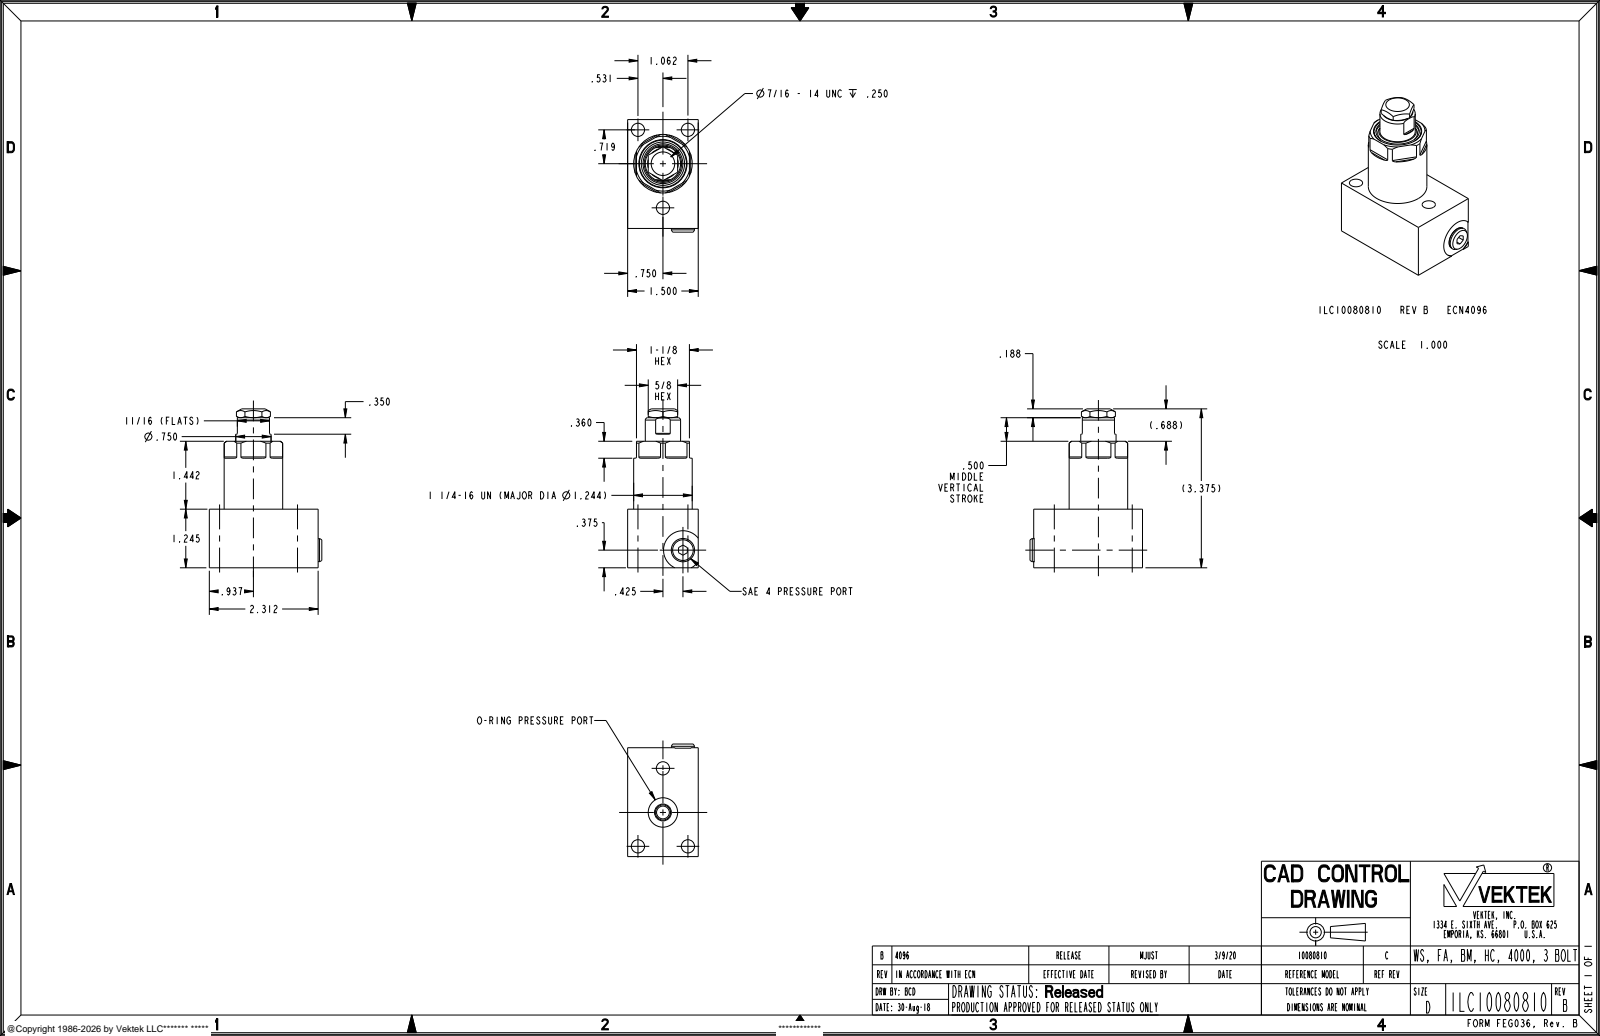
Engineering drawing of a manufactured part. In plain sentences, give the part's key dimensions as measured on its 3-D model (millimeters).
The part is named "ILC10080810". Its 3-D file was written by "PRO/ENGINEER BY PARAMETRIC TECHNOLOGY CORPORATION, 2017170 (AUTOMOTIVE_DESIGN)". It is 1 solid with 126 faces: 50 planar, 38 cylindrical and 38 other. Overall it measures 85.7 by 60.7 by 38.1 millimeters. Its volume is 97 220 cubic millimeters and its surface area 19 210 square millimeters. Round holes: 3 of diameter 7.1, 1 of diameter 6.9, 1 of diameter 9.3, 1 of diameter 10, 1 of diameter 15.9, 1 of diameter 23.4. Round bosses or shafts: 2 of diameter 11.1, 1 of diameter 31.6, 1 of diameter 25.4, 1 of diameter 19.1, 1 of diameter 11.1. Partial cylindrical surfaces (rounded edges, fillets, slot ends): 6 of radius 0.7, 2 of radius 0.5, 1 of radius 10.5. The main face-to-face distances are 38.1, 31.6, 58.7, 6.4, 28.6, 4.7, 33.4, 58.5, 22.2, 68.2. The hole center spacings are 22.7, 44.2, 23.8, 27.
